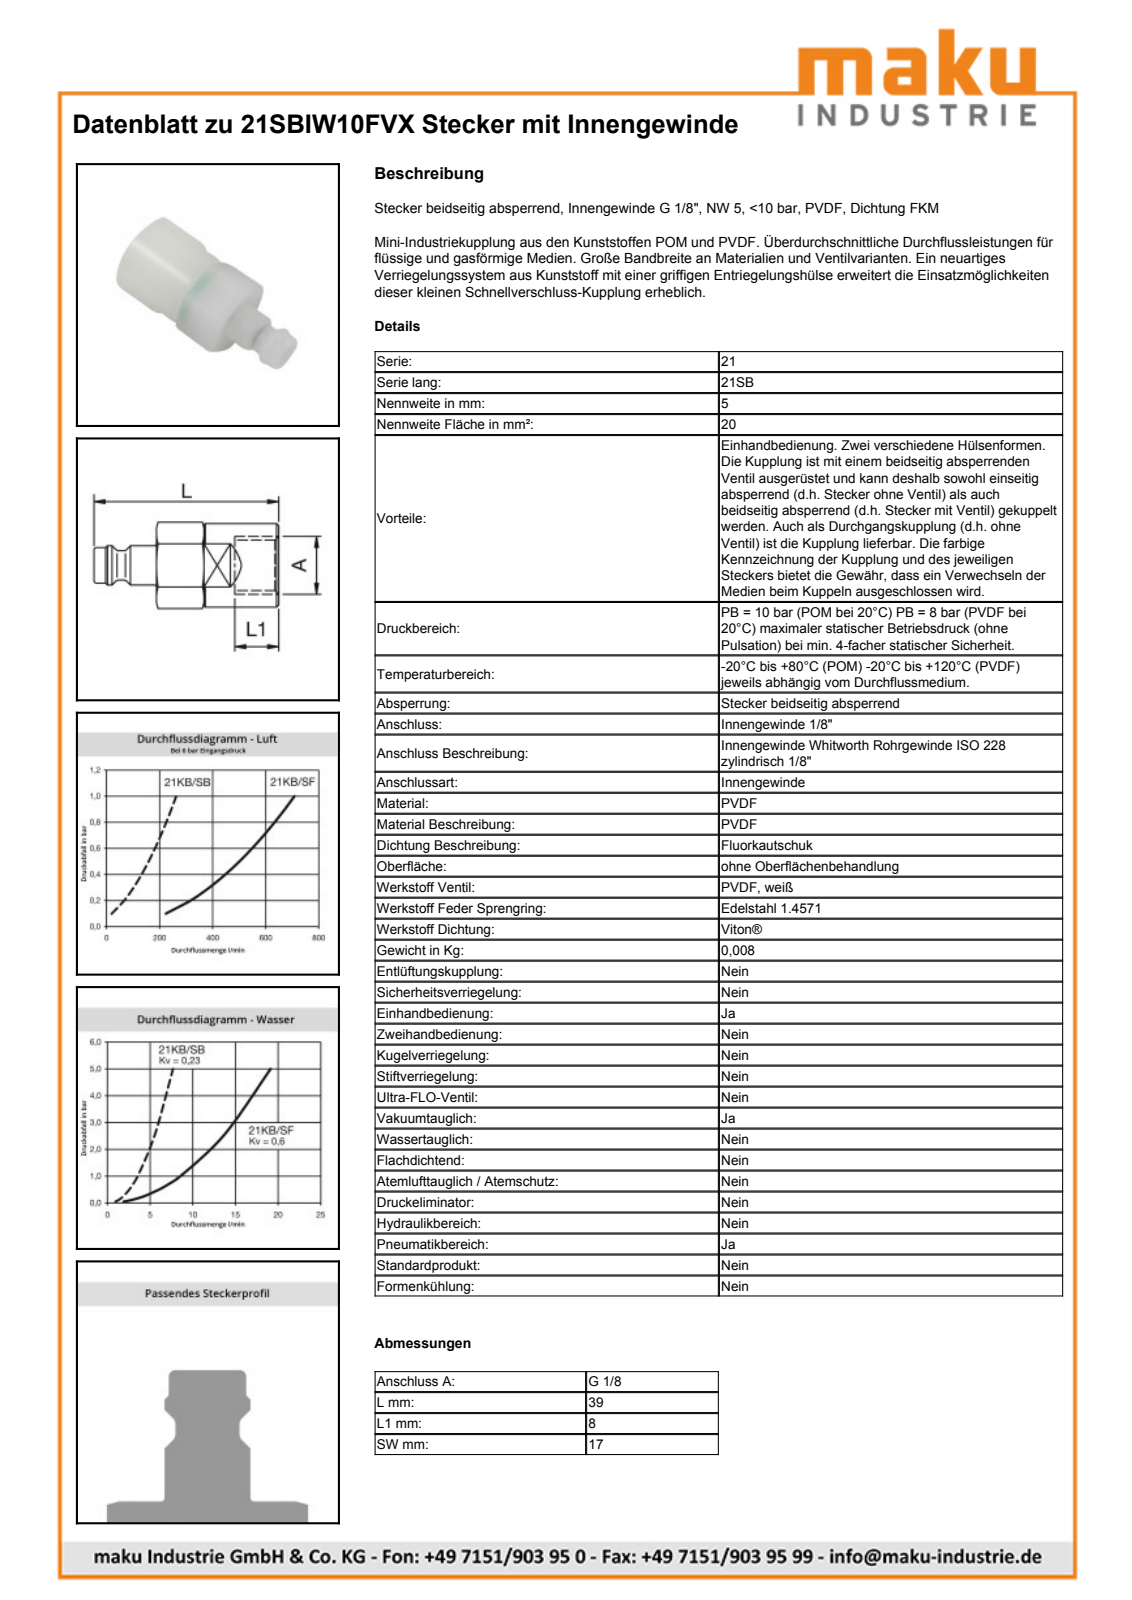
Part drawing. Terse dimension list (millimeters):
name: D109004
written by: Autodesk Inventor 2013 (AUTOMOTIVE_DESIGN)
unit: mm
bodies: 1 solid, 48 faces (13 planar, 16 cylindrical, 19 other)
size: 40 × 15.8 × 14.21
volume: 4 424 mm³; area: 2 420 mm²
holes: 1× ⌀8.57, 1× ⌀12
bosses: 1× ⌀14, 1× ⌀11.35, 1× ⌀9, 1× ⌀8.1, 1× ⌀6.7
rounds: 1× R7.9
face distances: 14, 8.99, 20, 16.91, 25.9, 14.1, 31.01, 40, 5.9, 11.01
